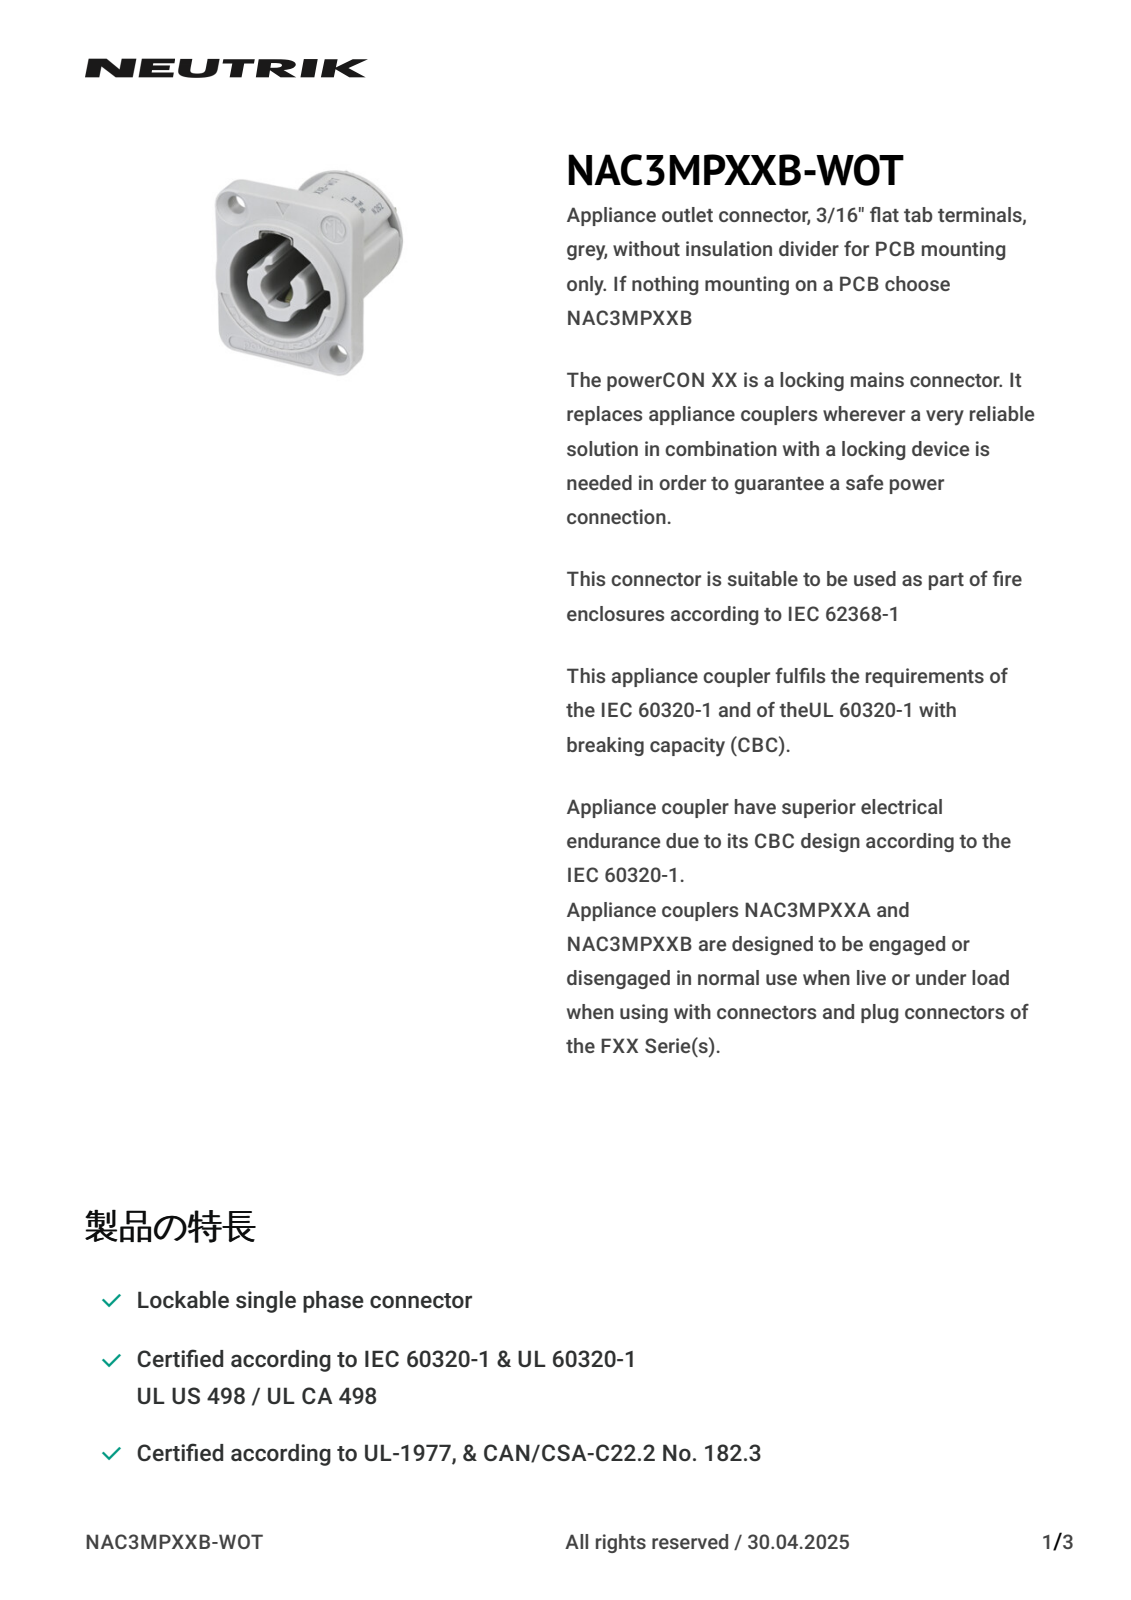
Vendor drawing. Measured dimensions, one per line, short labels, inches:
name: 30011244
written by: CREO PARAMETRIC BY PTC INC, 2021184 (CONFIG_CONTROL_DESIGN)
unit: in
bodies: 1 solid, 1242 faces (362 planar, 193 cylindrical, 687 other)
size: 1.35 × 1.217 × 1.02
volume: 0.418 in³; area: 11.37 in²
holes: 2× ⌀0.055, 2× ⌀0.236, 1× ⌀0.165, 1× ⌀0.197
bosses: 1× ⌀0.886, 1× ⌀0.144
rounds: 45× R0.008, 23× R0.02, 22× R0.012, 13× R0.01, 9× R0.008, 7× R0.006, 4× R0.039, 3× R0.011
face distances: 0.923, 0.1, 0.746, 0.177, 0.278, 1.024, 0.58, 0.167, 0.757, 0.857
hole spacings: 0.82, 0.431, 0.748, 0.945, 1.205
